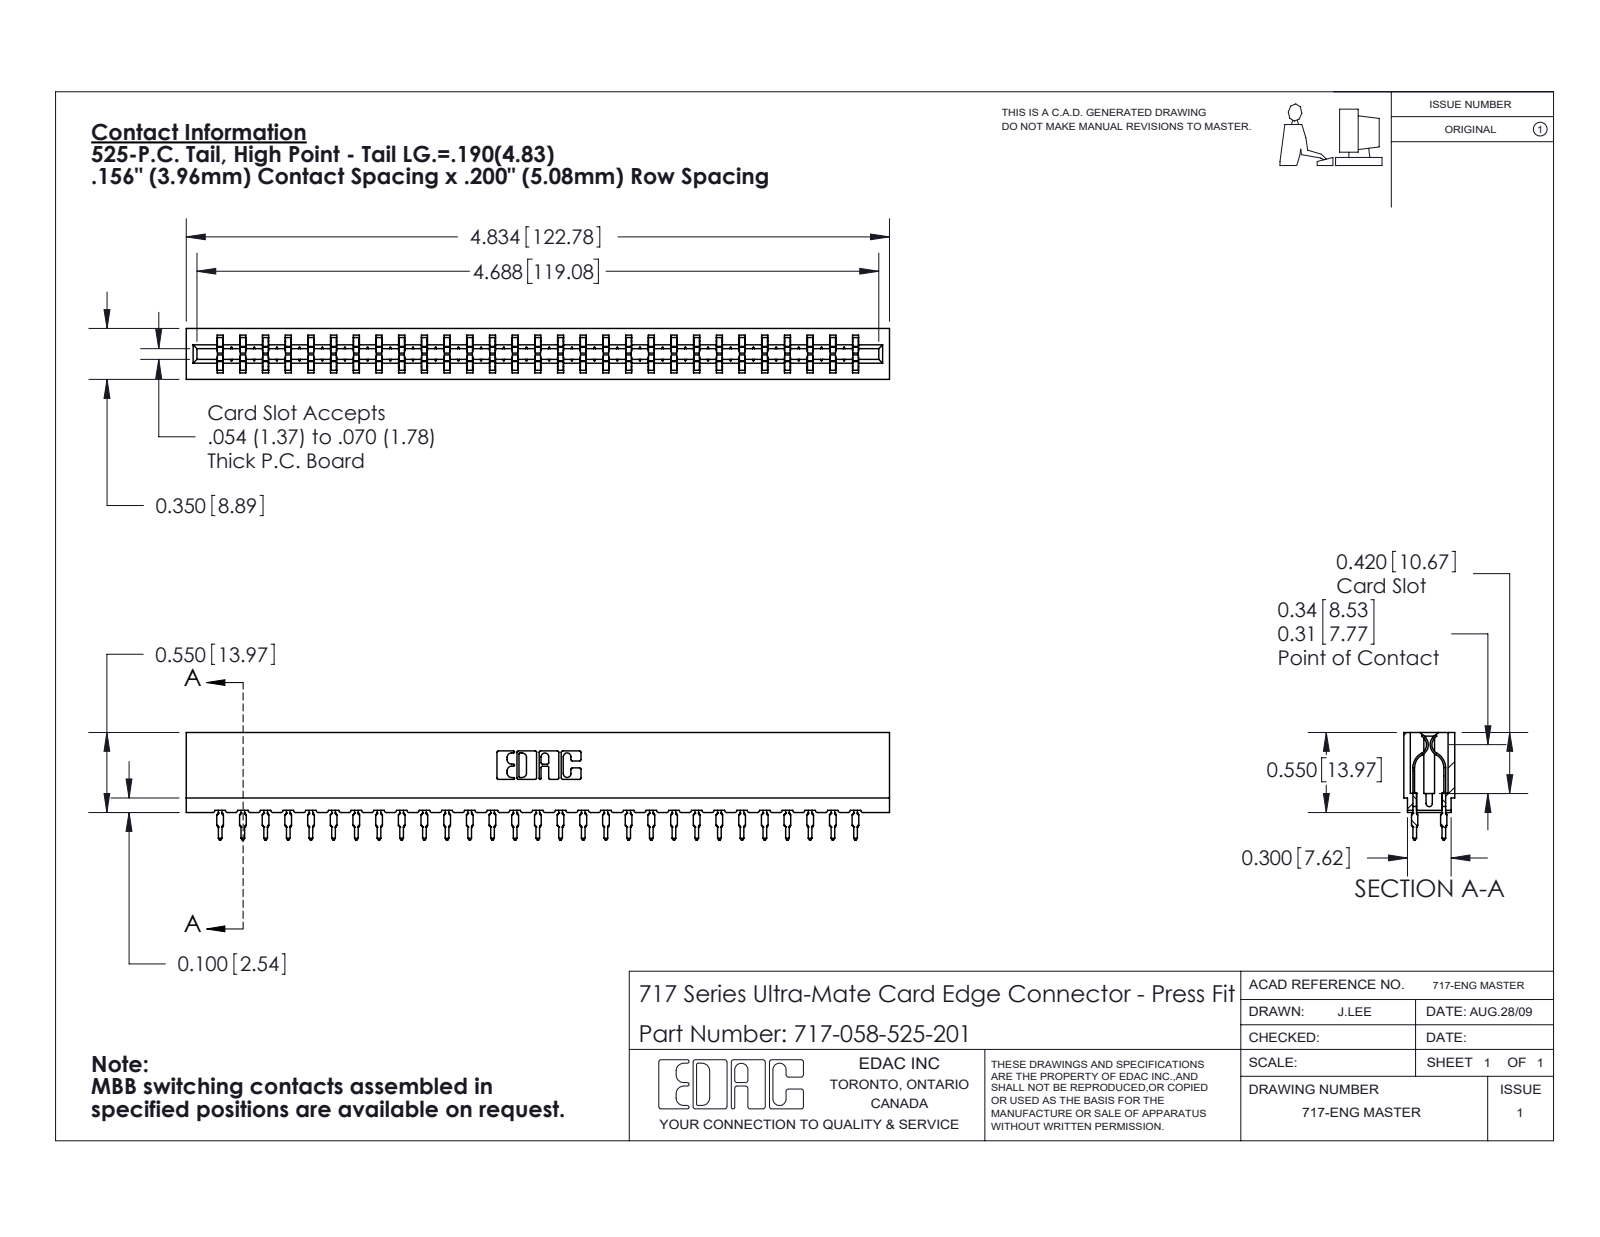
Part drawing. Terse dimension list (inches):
name: 745-292-001_525; 717-058-525-201; 717 Part_Insulator Option - 06
written by: SolidWorks 2020 (CONFIG_CONTROL_DESIGN)
unit: in
bodies: 59 solids, 5314 faces (2751 planar, 1055 cylindrical, 1508 other)
size: 4.834 × 0.739 × 0.35
volume: 0.652 in³; area: 24.95 in²
rounds: 116× R0.021, 58× R0.015, 22× R0.01, 8× R0.005, 8× R0.011, 6× R0.007, 6× R0.031, 3× R0.026
face distances: 0.212, 0.138, 0.35, 0.063, 0.287, 0.076, 0.149, 0.074, 0.156, 0.045
